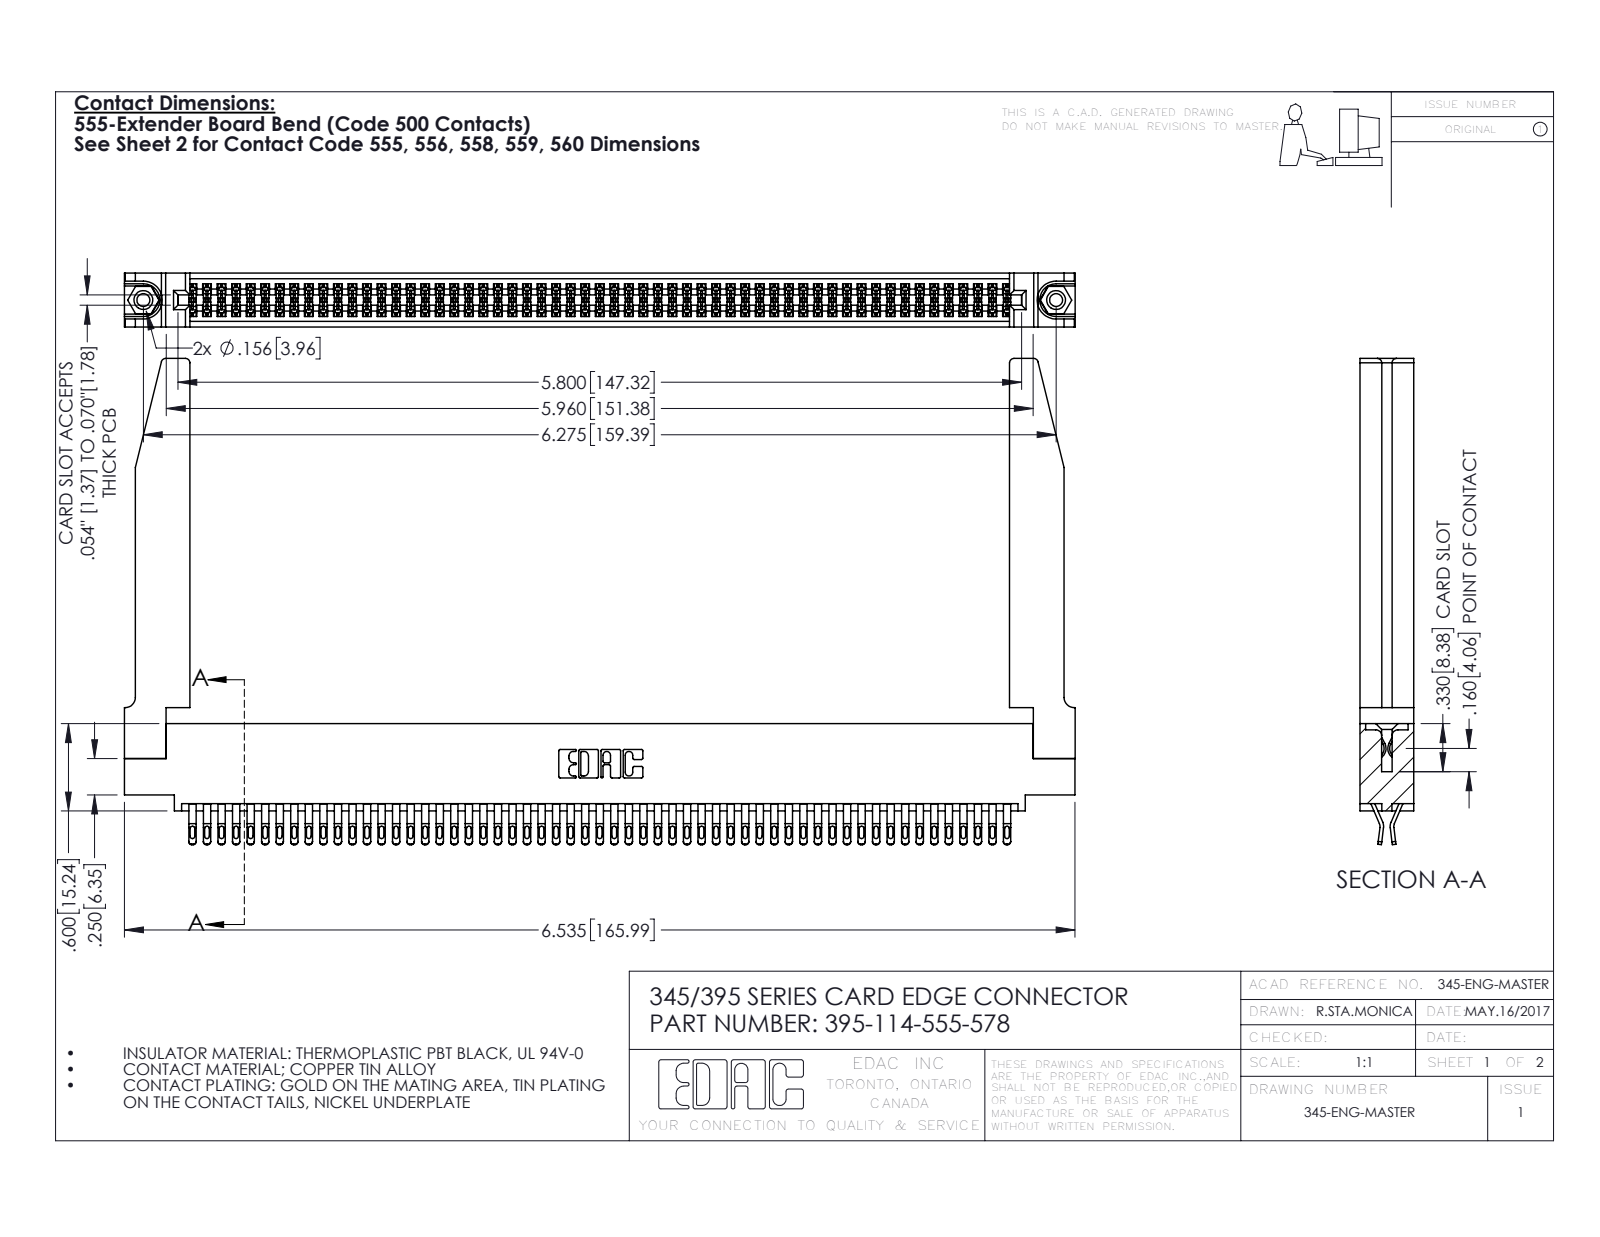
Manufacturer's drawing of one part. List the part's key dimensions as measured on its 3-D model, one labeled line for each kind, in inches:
Part name (STEP PRODUCT): 345-220-078_345-220-078; 345-292-001_555 Tail; 345-250-001_345-250-001-102; 395-114-555-578 (+1 more)
STEP written by: SolidWorks 2016 (CONFIG_CONTROL_DESIGN)
Units: inches
Bodies: 119 solids, 6748 faces (3760 planar, 2936 cylindrical, 52 other)
Overall size (bounding box): 6.536 × 3.342 × 0.37
Volume: 1.482 in³ · Surface area: 50.83 in²
Round holes (diameter × count): ⌀0.089 ×2, ⌀0.125 ×2, ⌀0.156 ×2, ⌀0.064 ×1
Round bosses / shafts (diameter × count): ⌀0.155 ×2
Partial cylindrical surfaces — rounded edges, fillets, slot ends (radius × count): R0.016 ×285, R0.02 ×228, R0.006 ×171, R0.01 ×22, R0.03 ×8, R0.007 ×6, R0.031 ×6, R0.026 ×3
Main face-to-face distances: 0.072, 0.37, 0.298, 0.025, 0.2, 0.098, 0.272, 0.225, 0.175, 0.148
Hole centre spacings: 0.27, 6.039, 6.275
